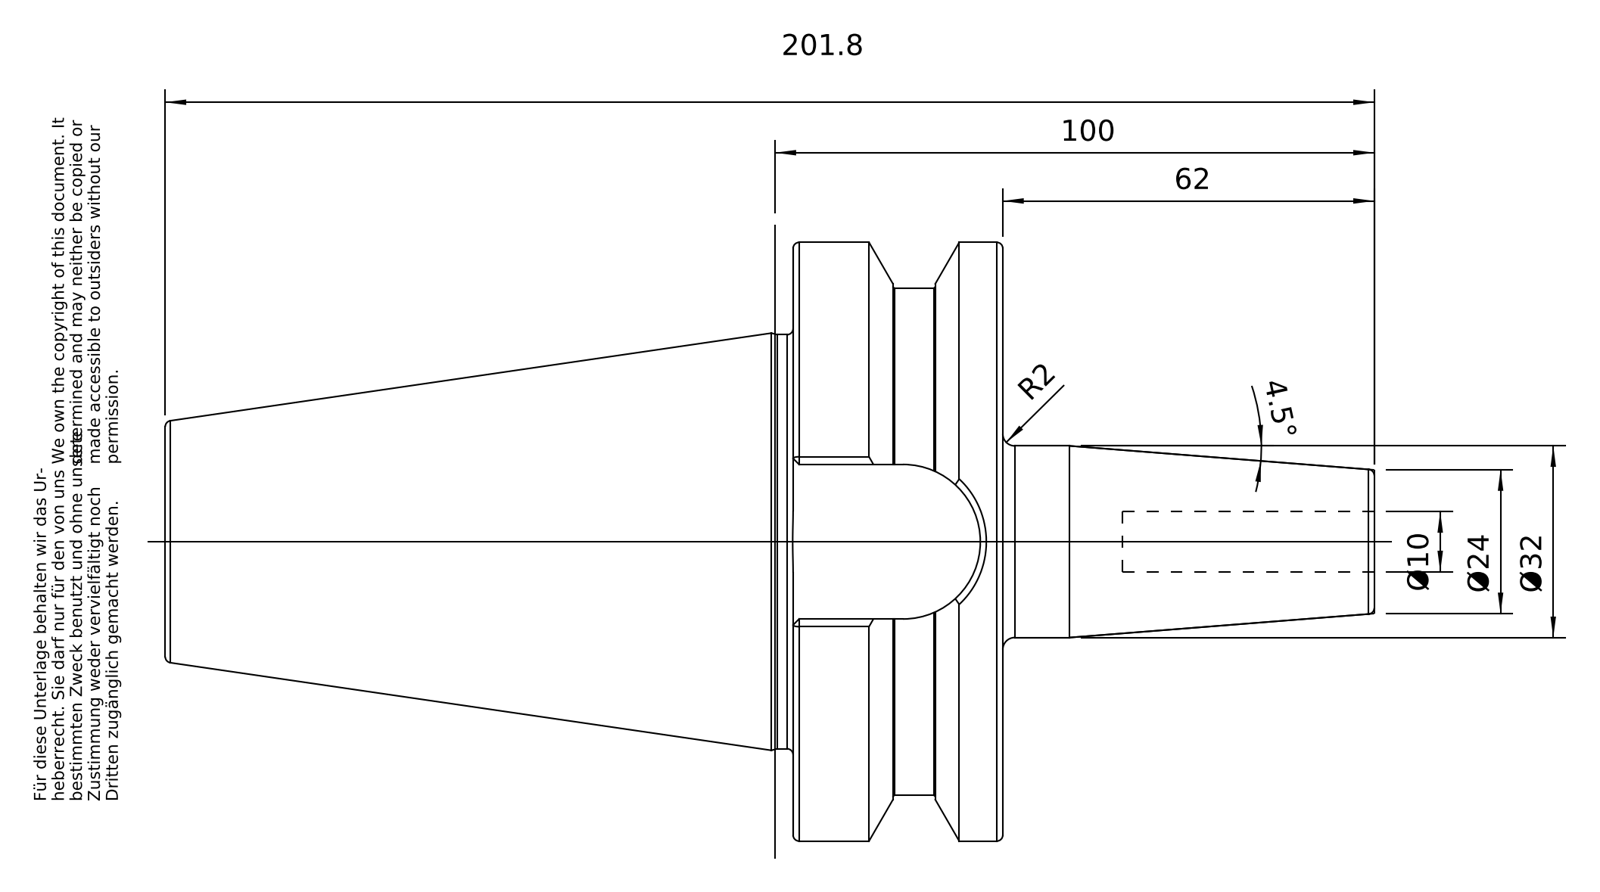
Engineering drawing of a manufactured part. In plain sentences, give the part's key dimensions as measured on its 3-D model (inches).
The part is named "50-640-10". Its 3-D file was written by "PRO/ENGINEER BY PARAMETRIC TECHNOLOGY CORPORATION, 2010430 (CONFIG_CONTROL_DESIGN)". It is 1 solid with 96 faces: 26 planar, 22 cylindrical and 48 other. Overall it measures 7.945 by 3.936 by 3.936 inches. Its volume is 30.84 cubic inches and its surface area 90.38 square inches. Round holes: 1 of diameter 0.394, 1 of diameter 0.817, 1 of diameter 0.985, 1 of diameter 1.012. Round bosses or shafts: 1 of diameter 3.936, 1 of diameter 3.337, 1 of diameter 2.722, 1 of diameter 1.26, 1 of diameter 0.945. Partial cylindrical surfaces (rounded edges, fillets, slot ends): 1 of radius 0.508. The main face-to-face distances are 1.378, 2.772, 4.126, 5.504, 1.016, 7.945, 3.819, 2.441, 1.89, 2.236.
